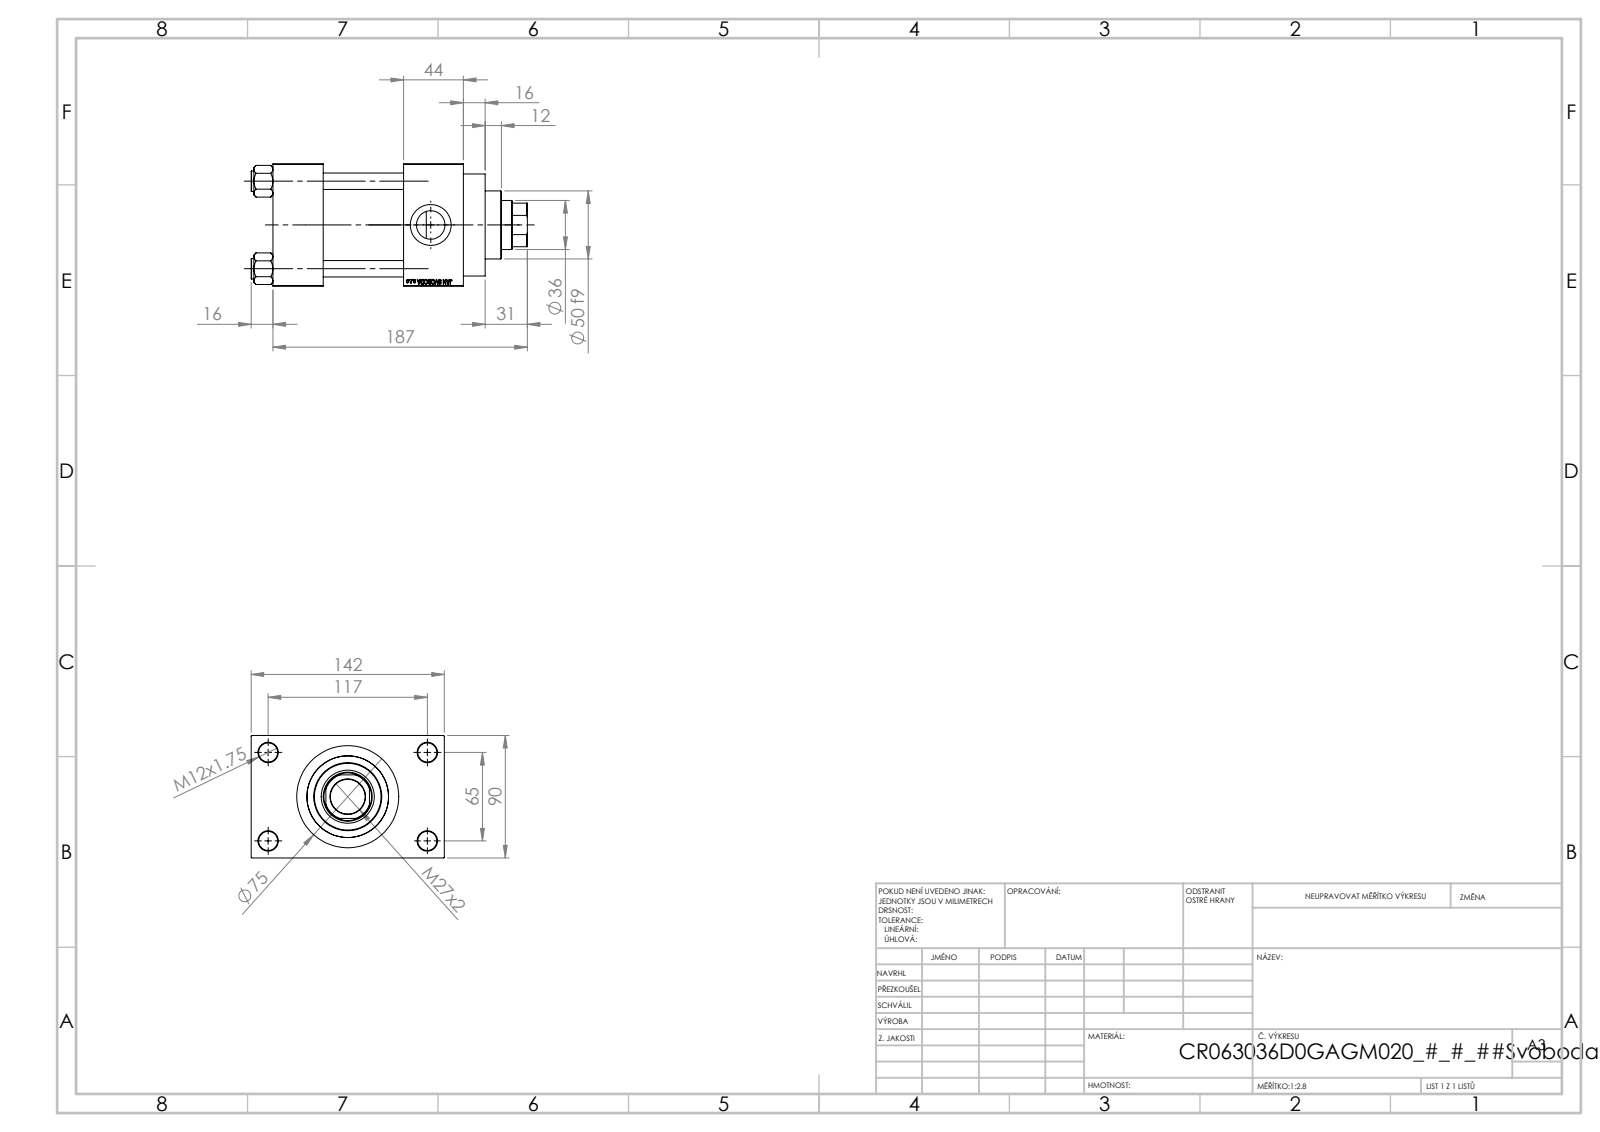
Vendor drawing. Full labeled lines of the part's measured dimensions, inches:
Part name (STEP PRODUCT): V215CR_D_Body; NUT_M5_D; V215CR_D_TYCINKA; V215_VC_A (+1 more)
STEP written by: SolidWorks 2019 (CONFIG_CONTROL_DESIGN)
Units: inches
Bodies: 11 solids, 1104 faces (497 planar, 89 cylindrical, 518 other)
Overall size (bounding box): 7.992 × 5.591 × 3.543
Volume: 67.8 in³ · Surface area: 319 in²
Round holes (diameter × count): ⌀0.472 ×4, ⌀0.551 ×4, ⌀0.276 ×2, ⌀0.825 ×2, ⌀1.181 ×2, ⌀1.004 ×1, ⌀1.417 ×1, ⌀1.535 ×1, ⌀1.969 ×1, ⌀2.362 ×1, ⌀2.48 ×1
Round bosses / shafts (diameter × count): ⌀0.591 ×4, ⌀2.953 ×1, ⌀2.717 ×1
Partial cylindrical surfaces — rounded edges, fillets, slot ends (radius × count): R0.689 ×1
Main face-to-face distances: 3.543, 2.323, 1.457, 3.78, 5.512, 4.055, 1.732, 1.024, 4.567, 5.591
Hole centre spacings: 1.037, 1.79, 2.531, 2.635, 2.748, 3.569, 4.383, 2.559
